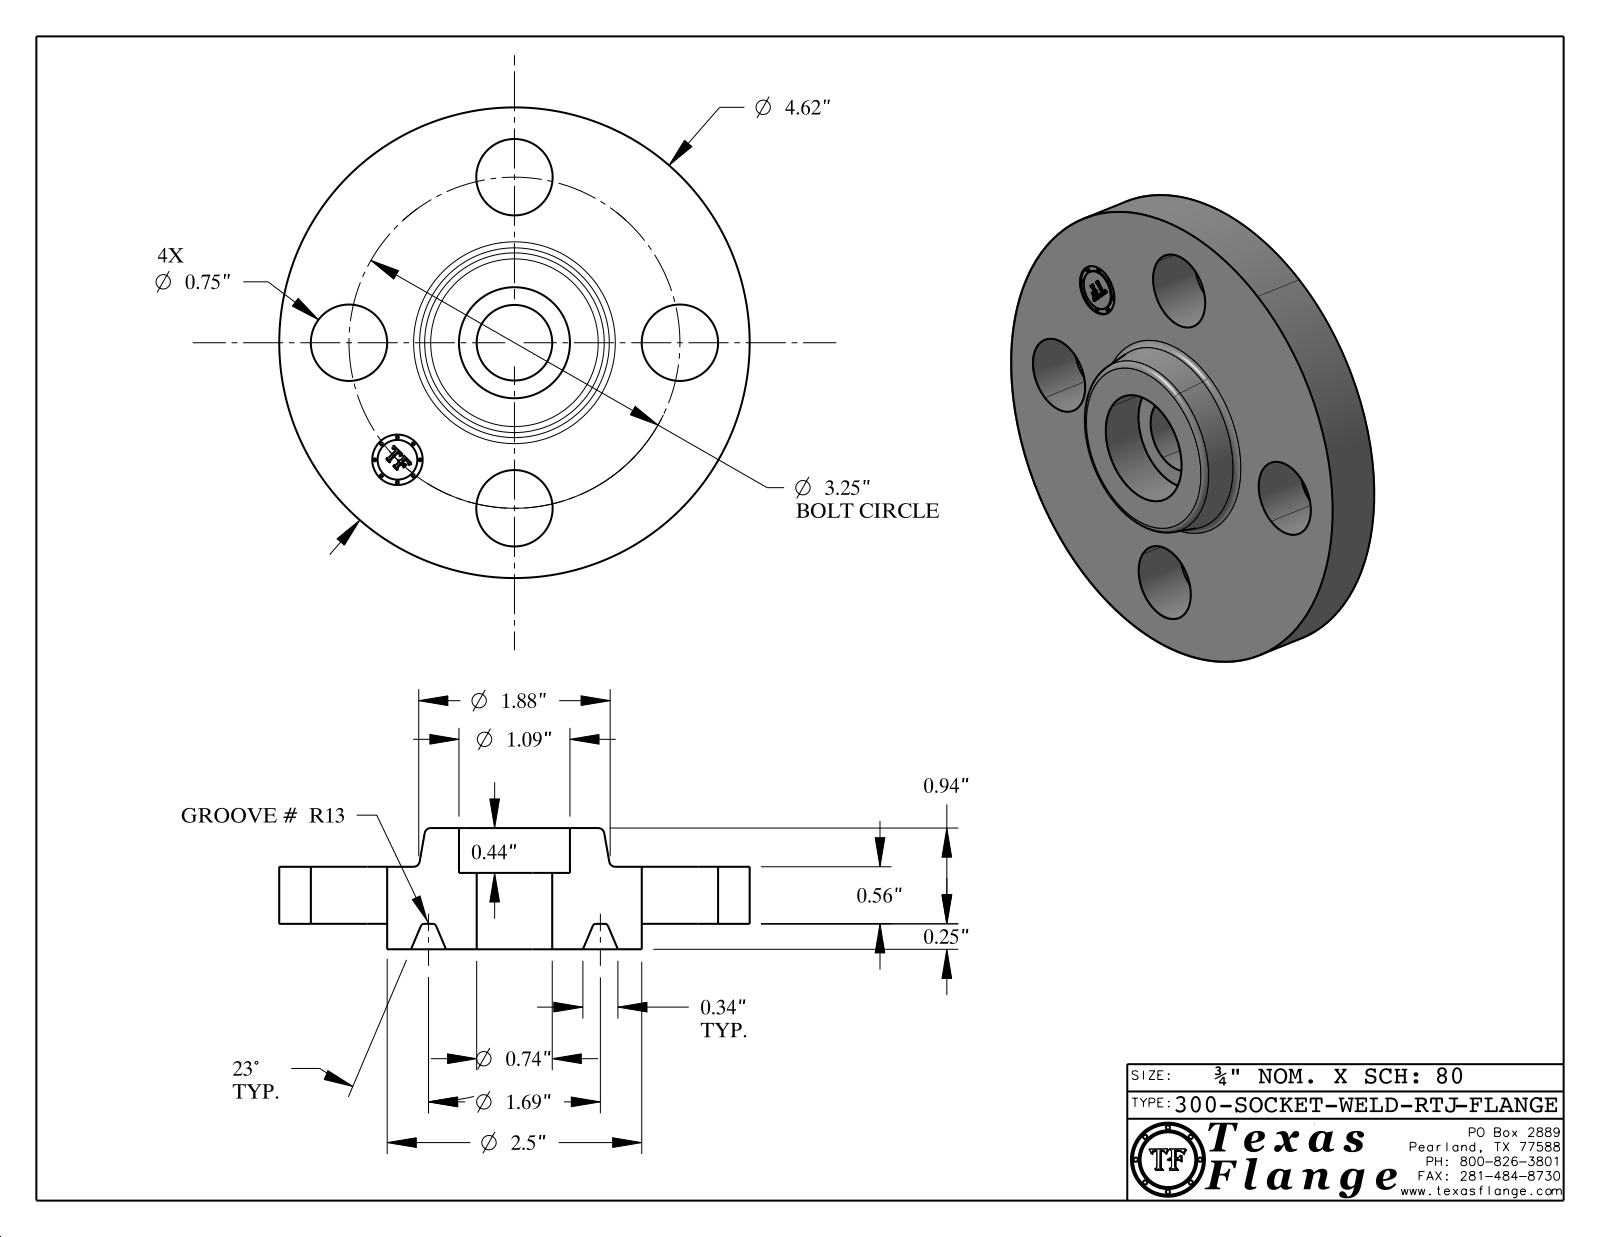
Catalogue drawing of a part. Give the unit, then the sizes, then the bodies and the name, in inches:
Units: inches
Overall size (bounding box): 4.62 × 4.62 × 1.19
Round holes (diameter × count): ⌀0.75 ×4, ⌀0.495 ×1, ⌀0.742 ×1, ⌀1.09 ×1
Round bosses / shafts (diameter × count): ⌀0.03 ×8, ⌀4.62 ×1, ⌀2.5 ×1, ⌀0.39 ×1
Main face-to-face distances: 0.56, 0.25, 0.81, 1.19, 0.94, 0.38, 0.75, 0.5, 0.06, 0.44
Hole centre spacings: 1.625, 2.298, 1.244, 3.003, 3.25
Volume: 9.556 in³ · Surface area: 51.17 in²
Bodies: 1 solid, 422 faces (372 planar, 36 cylindrical, 14 other)
Part name (STEP PRODUCT): 300-SOCKET-WELD-RTJ
STEP written by: CATIA V5 STEP AP214 (AUTOMOTIVE_DESIGN)
